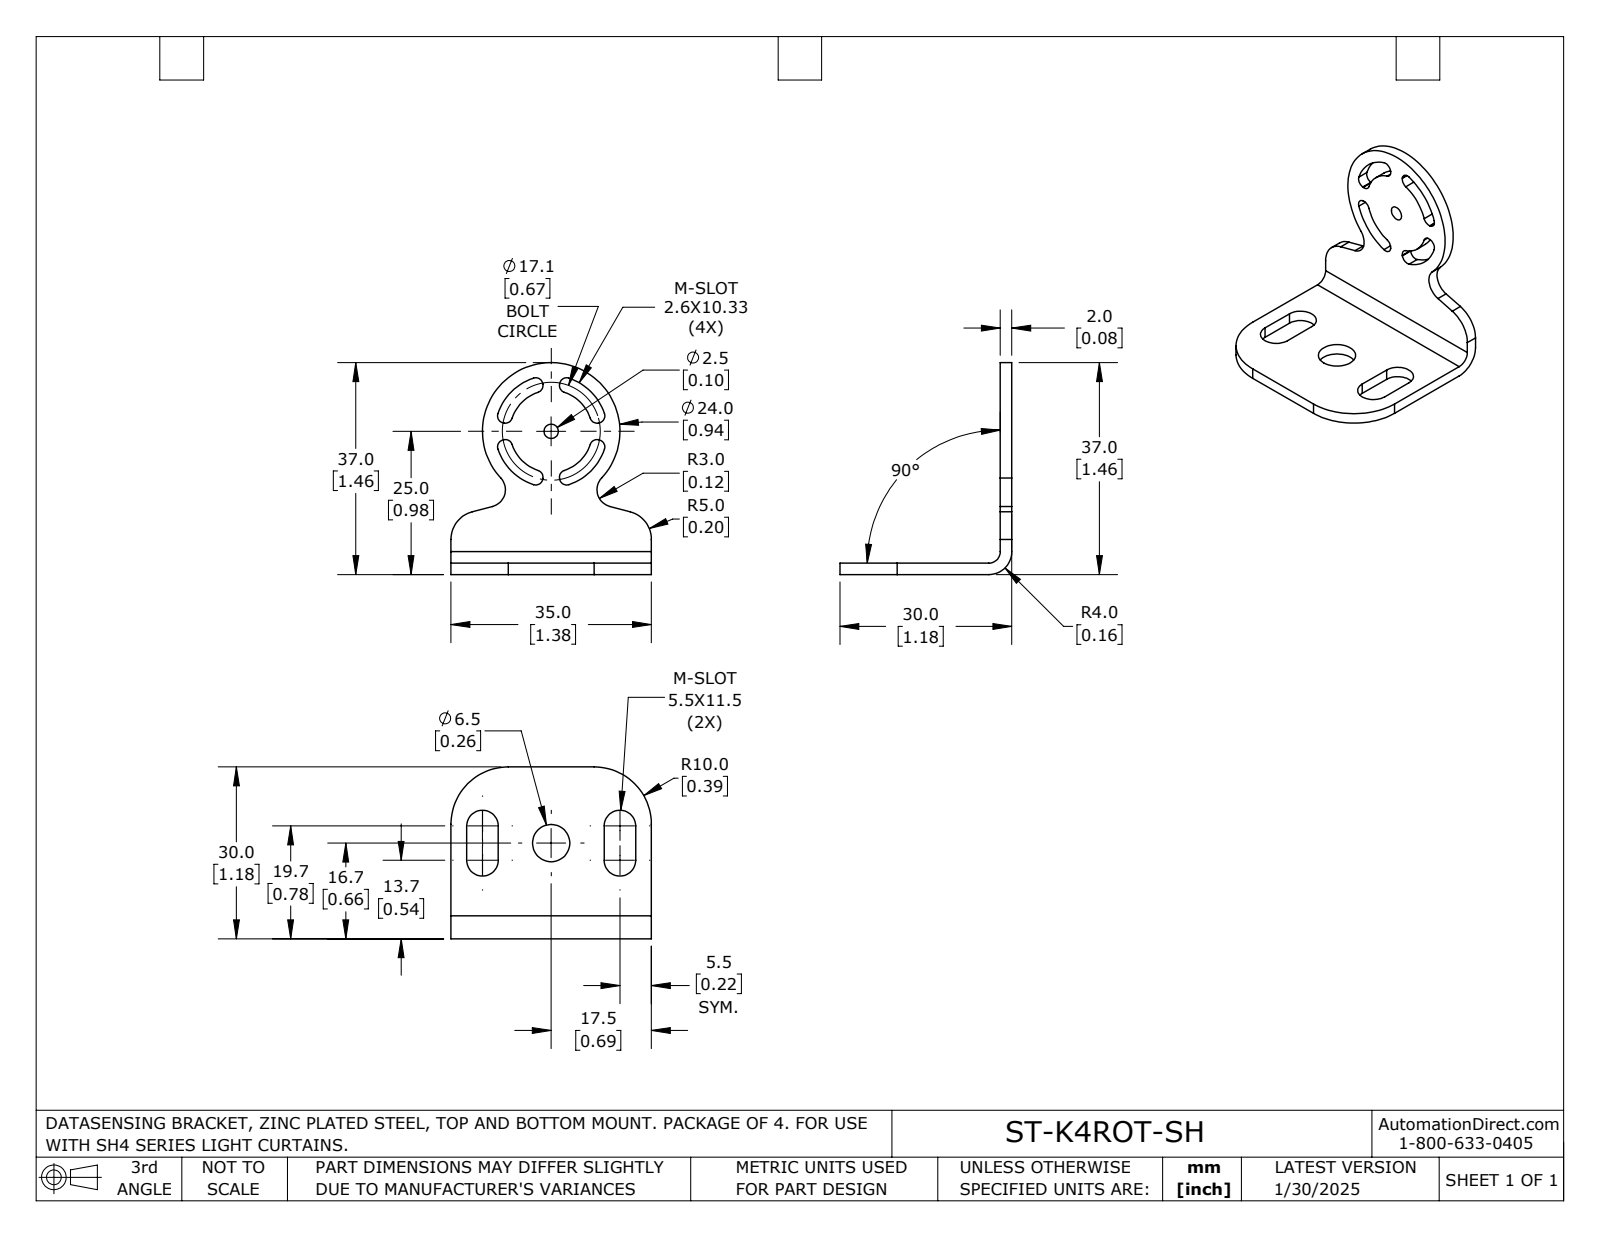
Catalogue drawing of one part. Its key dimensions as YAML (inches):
part_name: "ST-K4ROT-SH"
step_written_by: "SolidWorks 2024 (AUTOMOTIVE_DESIGN)"
units: inches
bodies: {solids: 4, faces: 126, planar: 55, cylindrical: 45, other: 26}
overall_size: [1.457, 1.378, 1.339]
volume: 0.195
surface_area: 6.389
round_holes:
  - {diameter: 0.059, count: 1}
  - {diameter: 0.098, count: 1}
  - {diameter: 0.256, count: 1}
round_bosses_or_shafts:
  - {diameter: 0.177, count: 2}
  - {diameter: 0.094, count: 2}
partial_cylinders:
  - {radius: 0.049, count: 16}
  - {radius: 0.108, count: 4}
  - {radius: 0.118, count: 2}
  - {radius: 0.197, count: 2}
  - {radius: 0.394, count: 2}
  - {radius: 0.079, count: 1}
  - {radius: 0.157, count: 1}
  - {radius: 0.283, count: 1}
face_to_face_distances: [0.079, 1.378, 1.102, 1.181, 0.108, 1.27, 0.325, 1.053, 0.217, 0.945]
